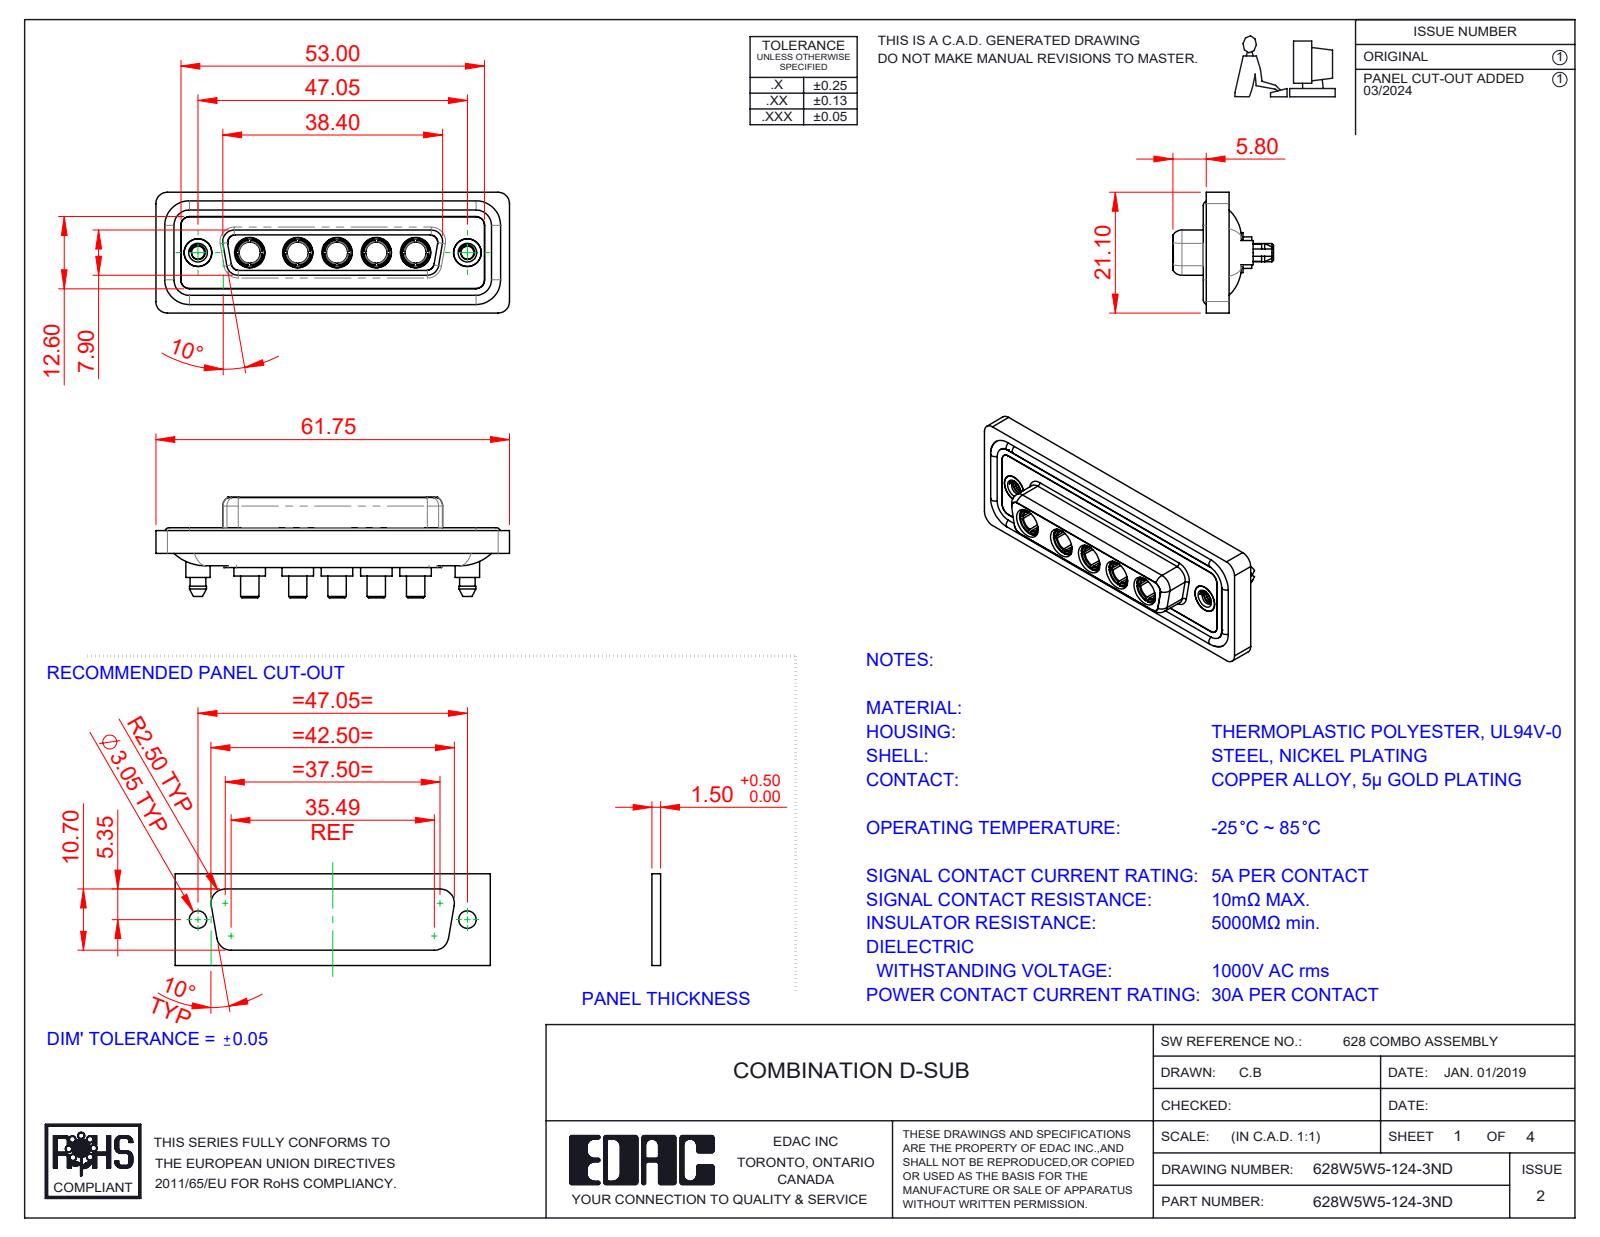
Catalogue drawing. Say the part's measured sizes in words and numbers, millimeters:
The part is named "628Combo Threaded Boardlock_D; 628Combo Shell Rear_25 Contacts; Power Socket_30A S; 628Combo Shell Front_25 Contacts (+3 more)". Its 3-D file was written by "SolidWorks 2023 (CONFIG_CONTROL_DESIGN)". It is 17 solids with 822 faces: 266 planar, 351 cylindrical and 205 other. Overall it measures 61.75 by 21.1 by 17.55 millimeters. Its volume is 8 343 cubic millimeters and its surface area 13 778 square millimeters. Round holes: 7 of diameter 4.85, 5 of diameter 3.7, 5 of diameter 5.3, 2 of diameter 2.26, 2 of diameter 4, 2 of diameter 4.05, 2 of diameter 5. Round bosses or shafts: 5 of diameter 5.5, 5 of diameter 5.2, 5 of diameter 4.96, 5 of diameter 4.75, 5 of diameter 3.75, 5 of diameter 3.2, 4 of diameter 1.6, 2 of diameter 5.4. Partial cylindrical surfaces (rounded edges, fillets, slot ends): 24 of radius 1.5, 18 of radius 2, 10 of radius 1.6, 8 of radius 1.35, 5 of radius 2.1, 4 of radius 0.25, 4 of radius 0.5, 4 of radius 0.6. The main face-to-face distances are 0.4, 1.8, 7.45, 5.65, 0.5, 7.05, 6.6, 1.6, 1.1, 2.9. The hole center spacings are 6.86, 9.04, 13.72, 38.01, 8.39, 15.25, 15.9, 17.43.
